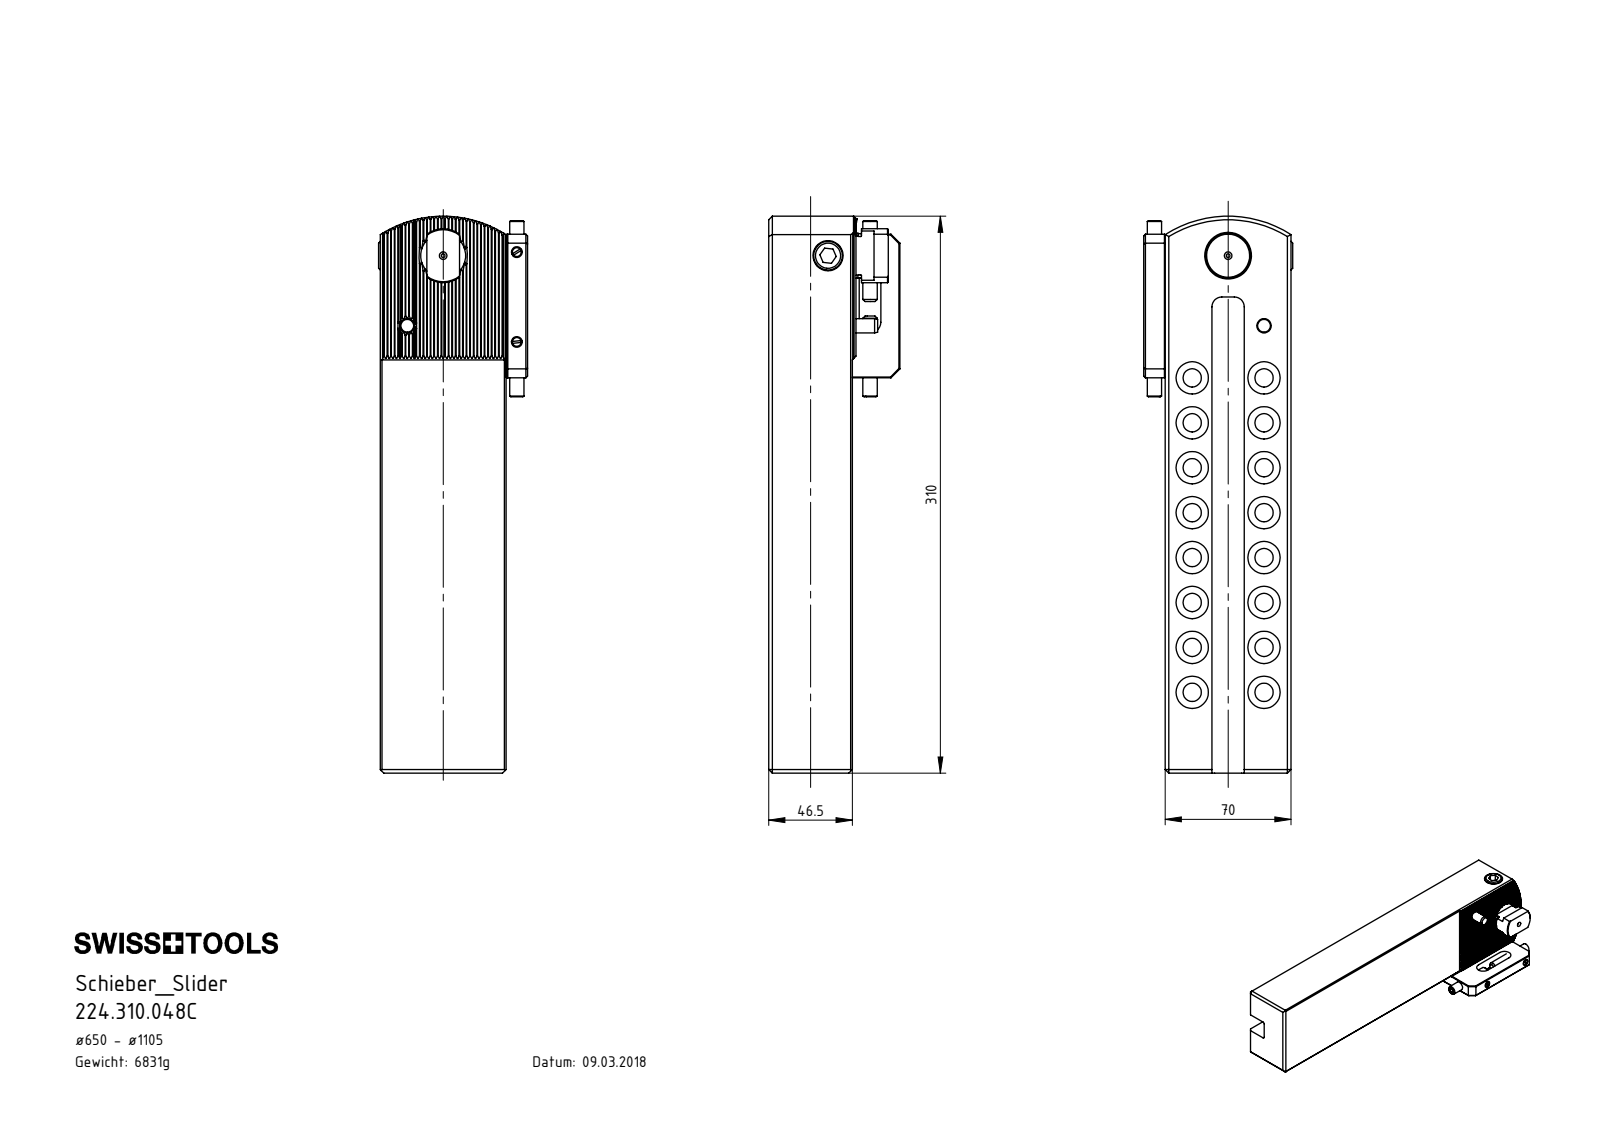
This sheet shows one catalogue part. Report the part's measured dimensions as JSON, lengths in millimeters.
{"part_name": "VK3-VK1.310.048_B; VK1-ER2.201.010_A_vorgespannt; VK1-ER2.101.010_A; VK1-ER1.001.030_A (+8 more)", "step_written_by": "SolidWorks 2017 (CONFIG_CONTROL_DESIGN)", "units": "millimeters", "bodies": {"solids": 13, "faces": 695, "planar": 311, "cylindrical": 239, "other": 145}, "overall_size": [310, 83.5, 73], "volume_mm3": 870762, "surface_area_mm2": 143981, "round_holes": [[18, 17], [10.2, 16], [5, 2], [6, 2], [6.8, 2], [2, 1], [8, 1], [8.5, 1], [10.5, 1], [11, 1], [14, 1], [25, 1]], "round_bosses_or_shafts": [[16, 2], [6, 2], [10, 1]], "partial_cylinders_radius": [[0.14, 33], [2, 4], [1.5, 3], [5.5, 2], [6, 2], [12.3, 1], [15, 1], [65, 1]], "face_to_face_distances": [70, 46.5, 44, 26, 26.5, 18, 20, 12, 38, 56], "hole_center_spacings": [25, 47.17, 50, 64.03, 75, 85, 40, 100]}
